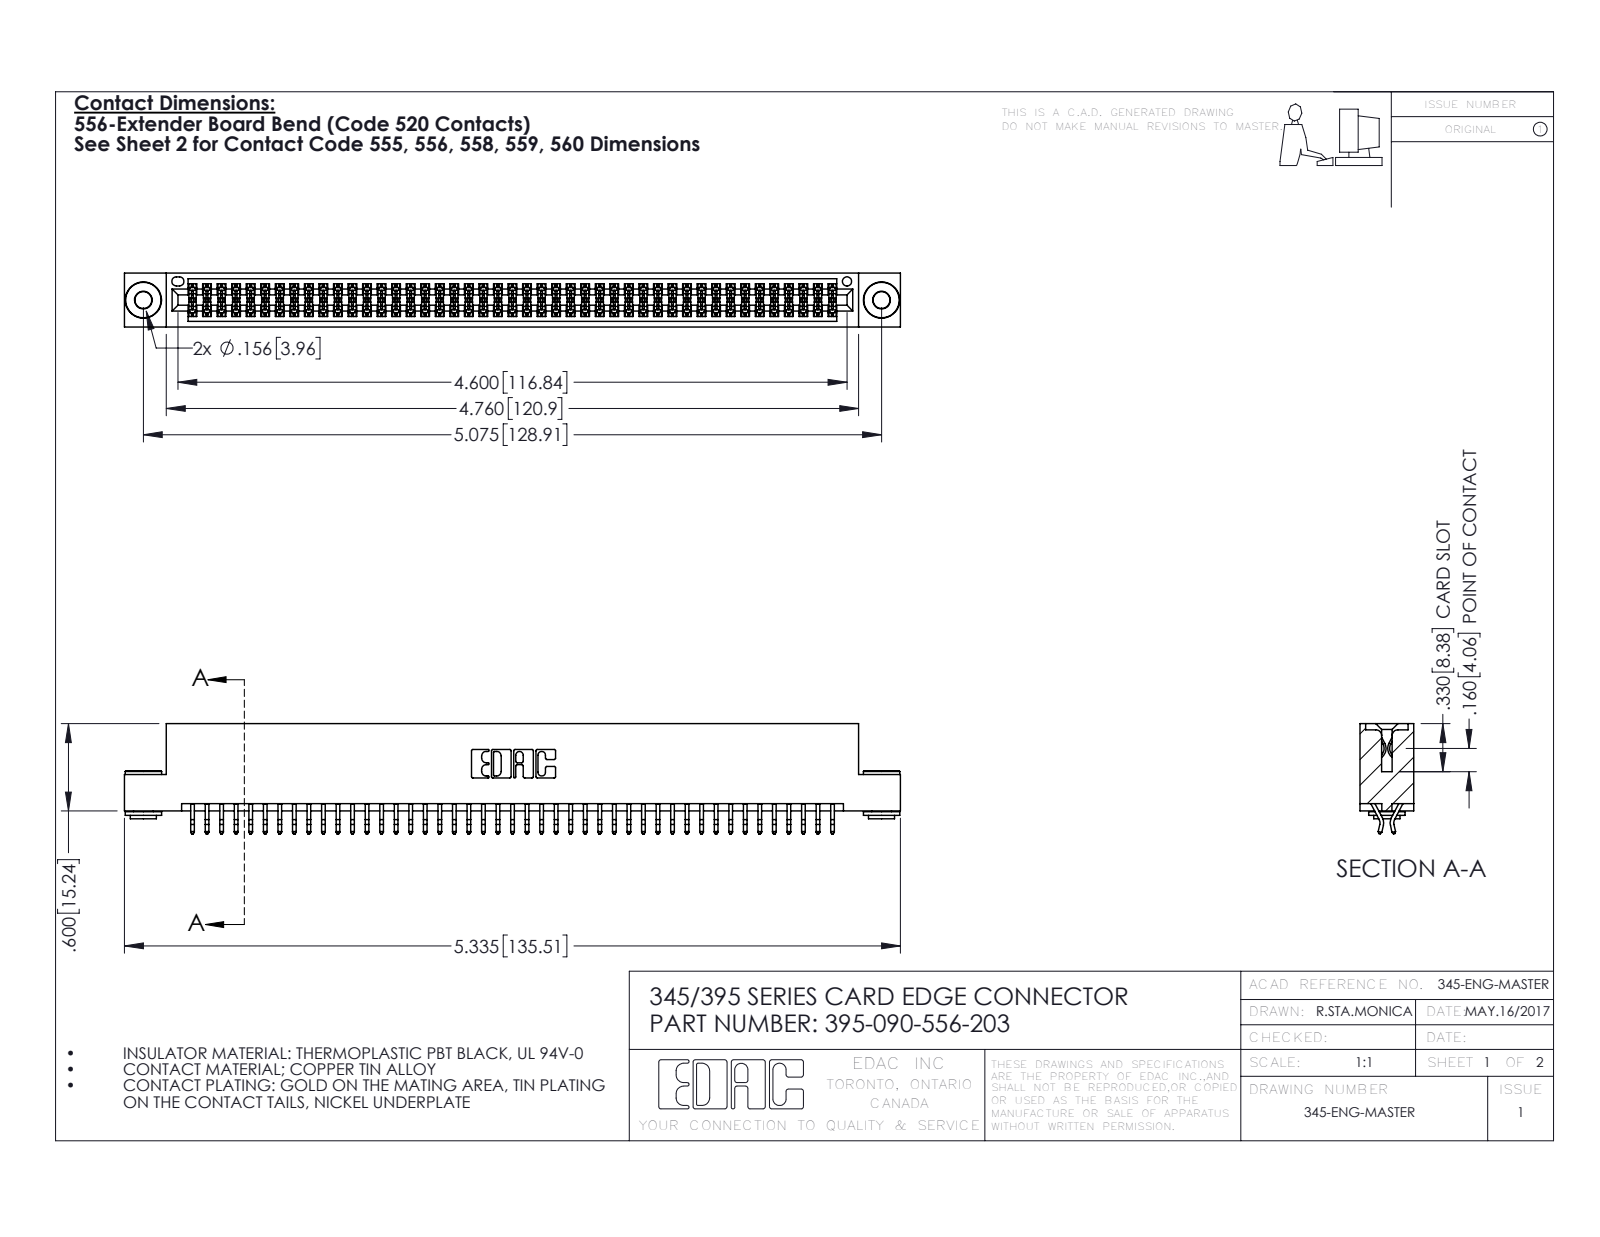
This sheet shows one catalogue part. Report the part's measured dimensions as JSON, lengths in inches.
{"part_name": "345-250-002_345-250-002-102; 345 Part_Flush Mounting Lugs - 0.156 Dia-TH; 345-292-001_556 Tail; 395-090-556-203", "step_written_by": "SolidWorks 2016 (CONFIG_CONTROL_DESIGN)", "units": "inches", "bodies": {"solids": 93, "faces": 5204, "planar": 3420, "cylindrical": 1776, "other": 8}, "overall_size": [5.335, 0.757, 0.37], "volume_in3": 0.806, "surface_area_in2": 30.55, "round_holes": [[0.116, 2], [0.156, 2], [0.064, 1]], "round_bosses_or_shafts": [[0.25, 2], [0.18, 2], [0.136, 2]], "partial_cylinders_radius": [[0.006, 135], [0.01, 22], [0.007, 6], [0.031, 6], [0.026, 3], [0.01, 2], [0.014, 2], [0.019, 2]], "face_to_face_distances": [0.072, 0.298, 0.2, 0.37, 0.025, 0.098, 0.272, 0.225, 0.175, 0.149], "hole_center_spacings": [0.27, 4.839, 5.075]}
